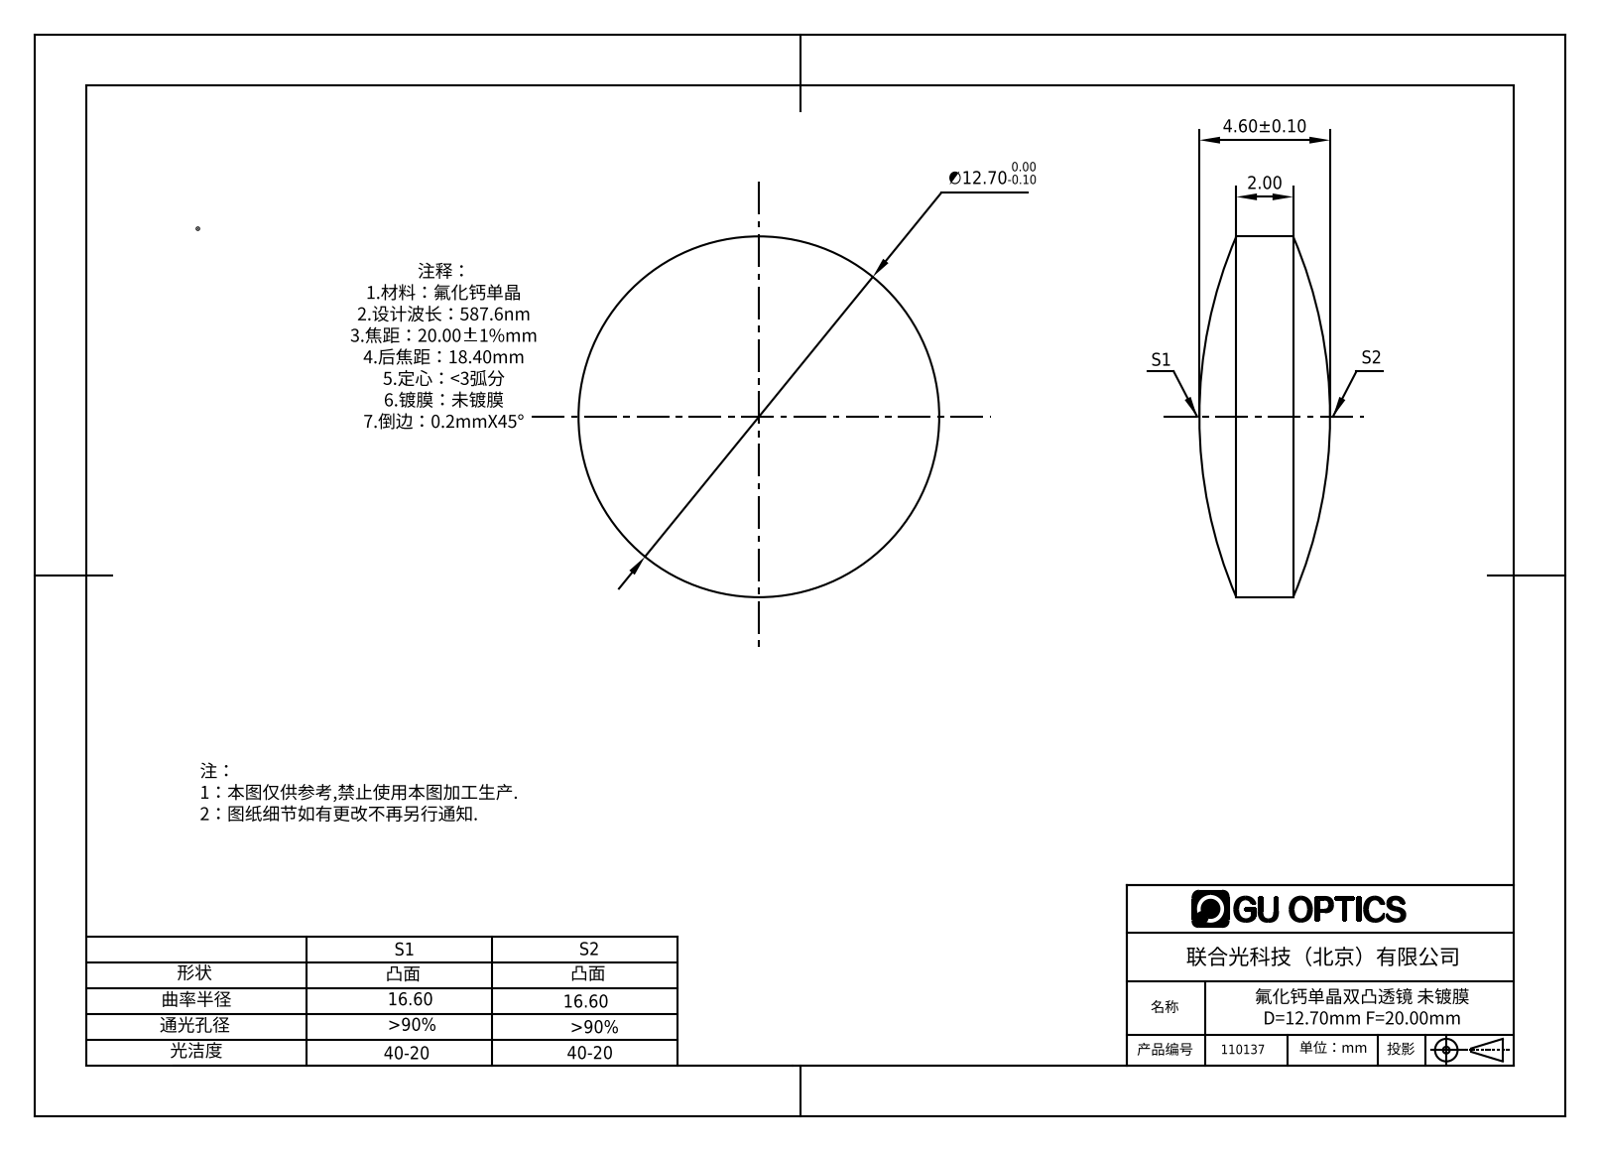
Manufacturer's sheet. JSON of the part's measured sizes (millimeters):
{"part_name": "110137", "step_written_by": "SolidWorks 2016 (CONFIG_CONTROL_DESIGN)", "units": "millimeters", "bodies": {"solids": 1, "faces": 6, "planar": 0, "cylindrical": 2, "other": 4}, "overall_size": [12.7, 12.7, 4.6], "volume_mm3": 420, "surface_area_mm2": 344, "round_bosses_or_shafts": [[12.7, 1]]}
